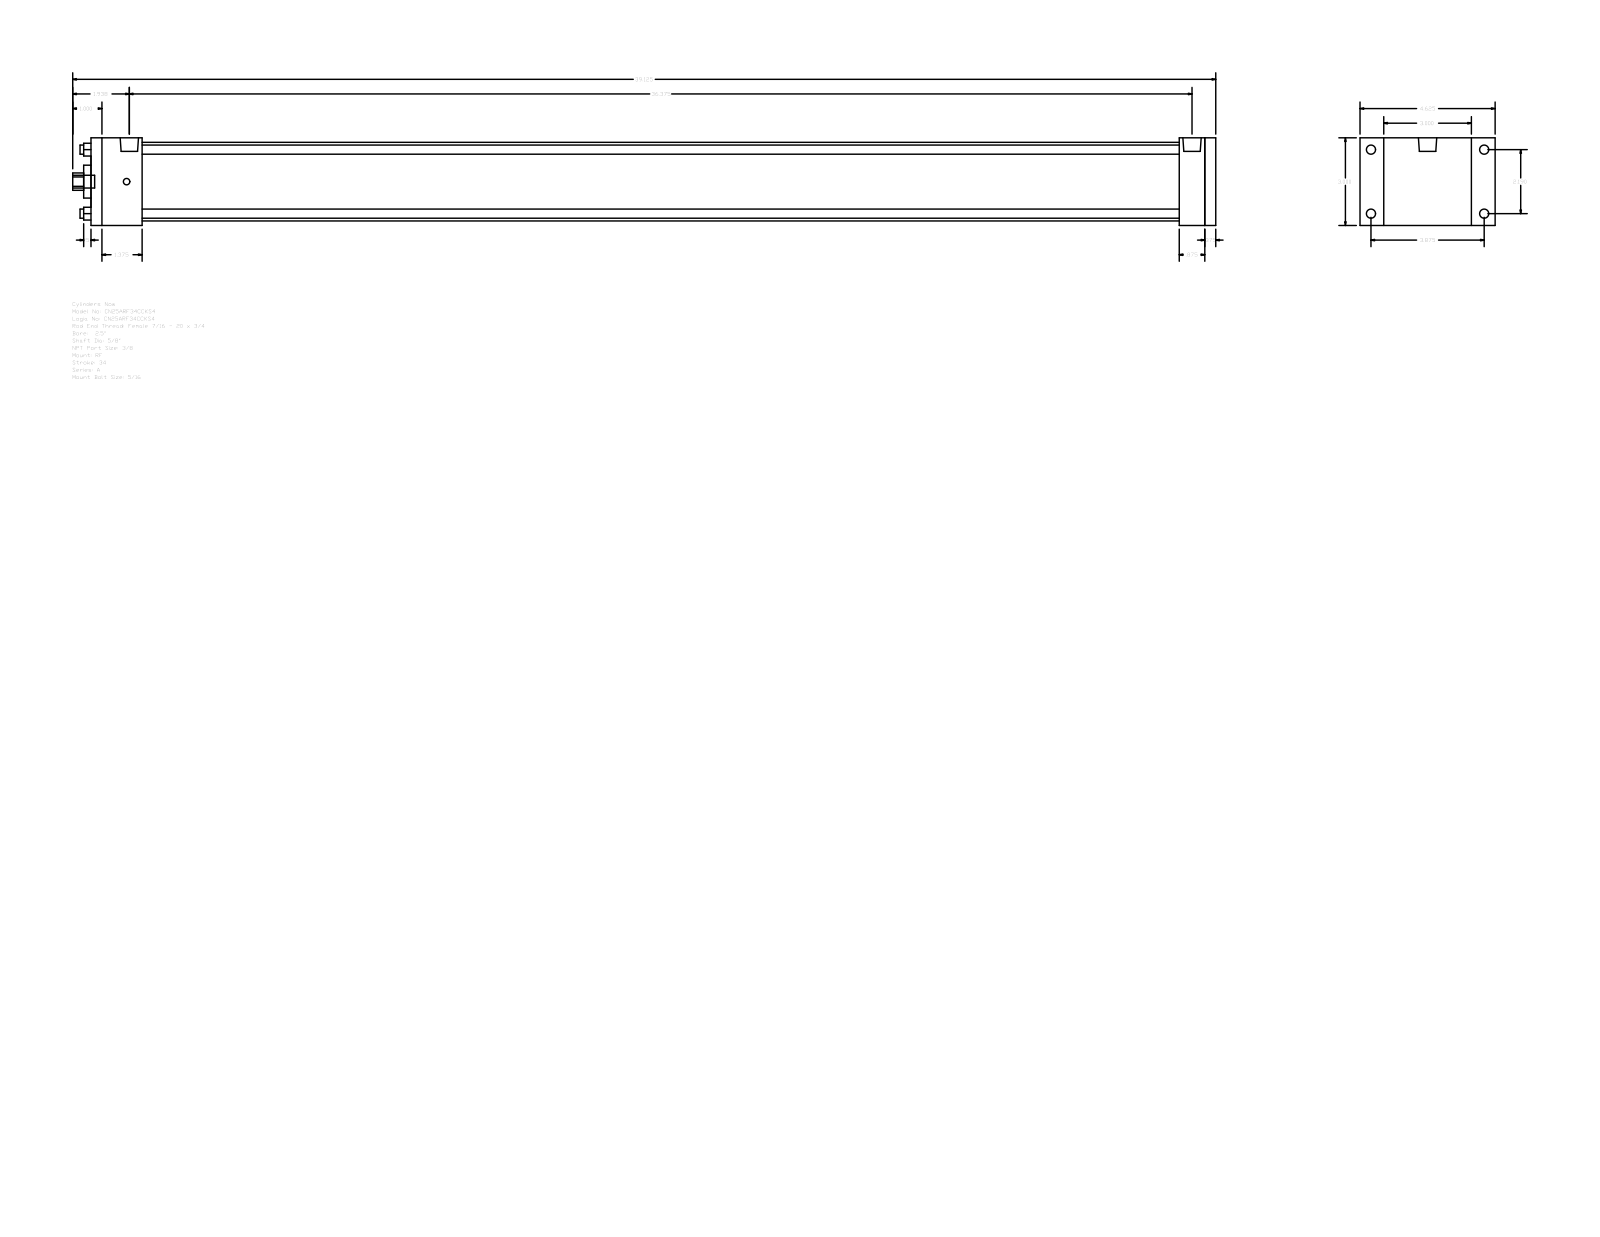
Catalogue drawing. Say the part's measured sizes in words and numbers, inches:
The part is named "A_RF__0250_0.625". Its 3-D file was written by "GSSL Pune (CONFIG_CONTROL_DESIGN)". It is 0 solids with 92 faces: 64 planar, 28 cylindrical and 0 other. Overall it measures 39.125 by 4.625 by 3 inches. Round holes: 4 of diameter 0.313, 1 of diameter 0.625, 1 of diameter 1.125, 1 of diameter 2.69. Round bosses or shafts: 4 of diameter 0.313, 4 of diameter 0.219, 2 of diameter 0.627, 1 of diameter 0.437. Partial cylindrical surfaces (rounded edges, fillets, slot ends): 1 of radius 0.297. The main face-to-face distances are 3, 38.5, 0.375, 38.125, 1.75, 1.25, 37.25, 35.5, 36.375, 36.75. The hole center spacings are 1.548, 2.19, 3.097.
